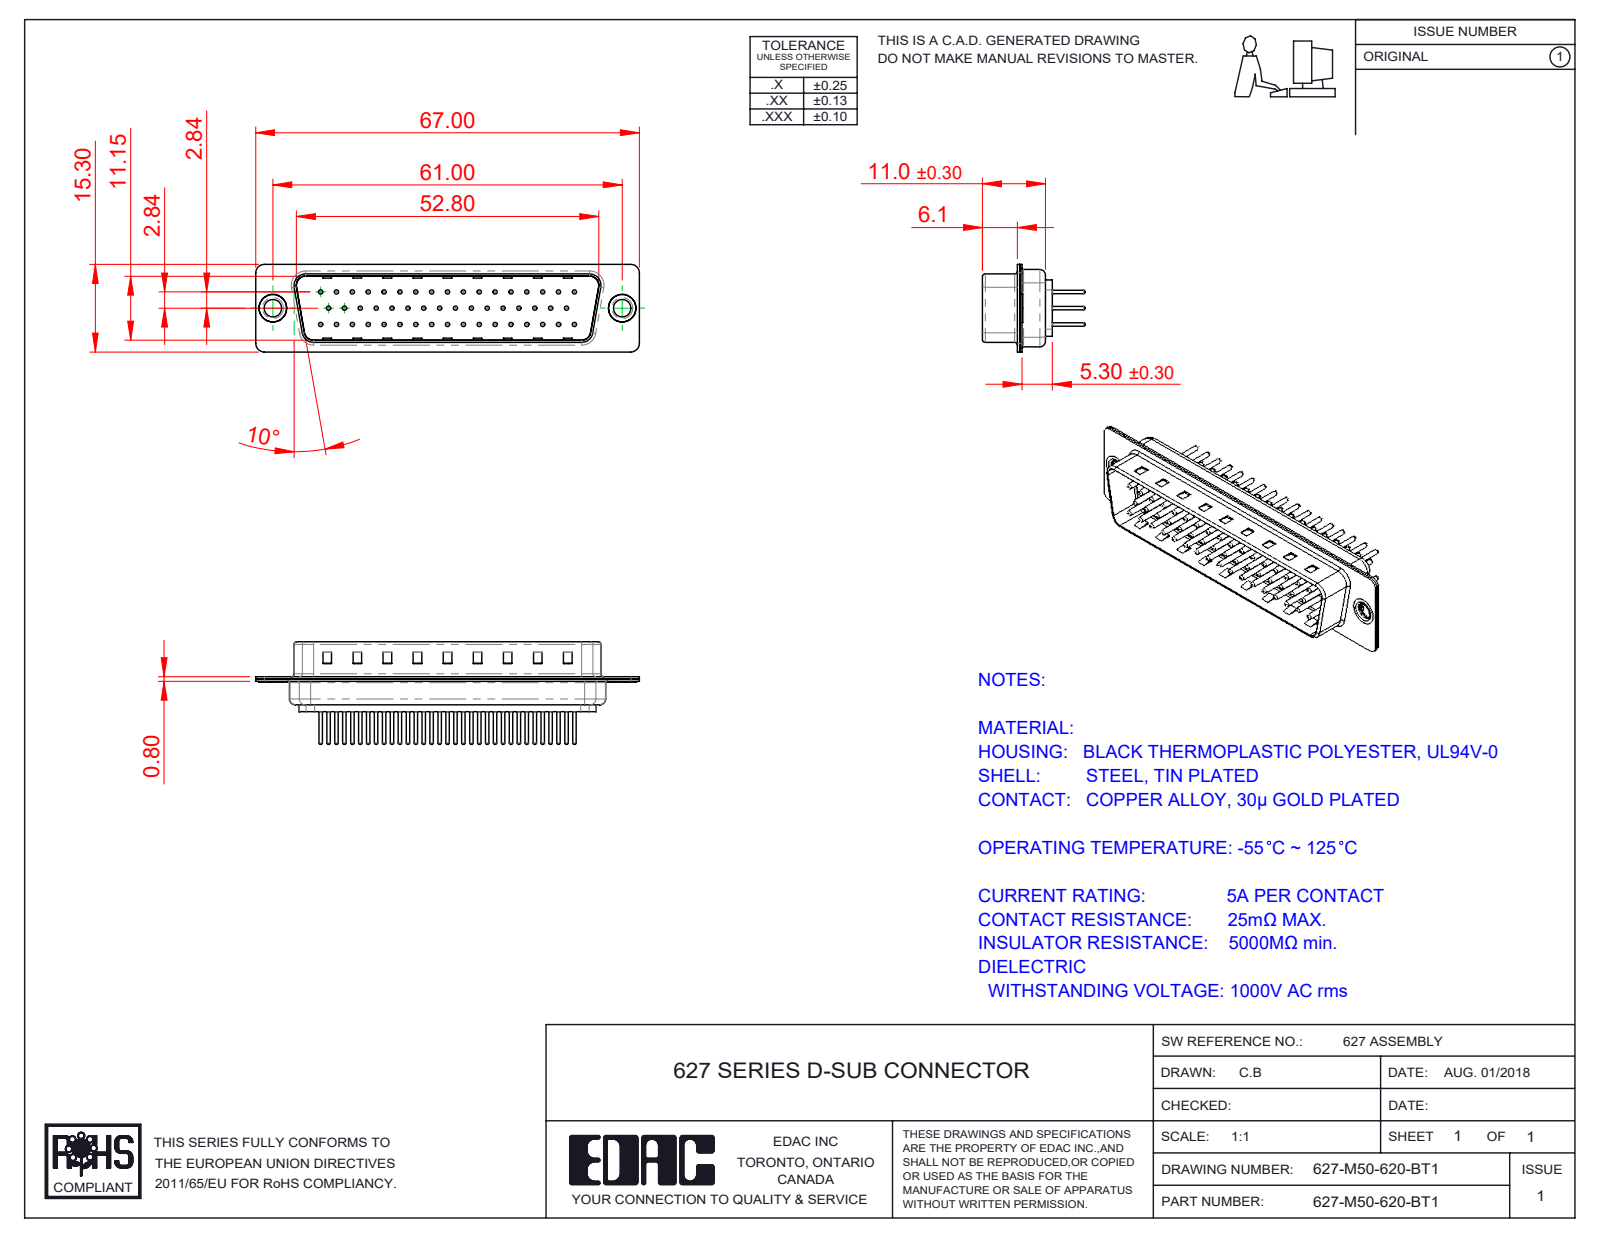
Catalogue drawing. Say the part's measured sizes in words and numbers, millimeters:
The part is named "627M Contact Row 3_20; 627M Shell Front_50 Contacts; 627M Thru Hole Rivet; 627M Contact Row 2_20 (+4 more)". Its 3-D file was written by "SolidWorks 2020 (CONFIG_CONTROL_DESIGN)". It is 55 solids with 2236 faces: 553 planar, 825 cylindrical and 858 other. Overall it measures 67 by 17.9 by 15.3 millimeters. Its volume is 4 447 cubic millimeters and its surface area 10 554 square millimeters. Round holes: 50 of diameter 0.75, 50 of diameter 1.6, 50 of diameter 2, 2 of diameter 3.05, 2 of diameter 4, 2 of diameter 4.8. Round bosses or shafts: 50 of diameter 1.5, 50 of diameter 0.6, 2 of diameter 5, 2 of diameter 4.9, 2 of diameter 3.55. Partial cylindrical surfaces (rounded edges, fillets, slot ends): 16 of radius 1.5, 12 of radius 2, 8 of radius 0.5, 8 of radius 1.6, 4 of radius 0.25, 4 of radius 0.6, 4 of radius 0.65, 4 of radius 0.9. The main face-to-face distances are 0.4, 11.55, 5.7, 6.1, 0.78, 0.77, 12.33, 12.32, 13.1, 5.3. The hole center spacings are 3.16, 2.77, 5.54, 8.31, 11.08, 13.85, 16.62, 5.03.
